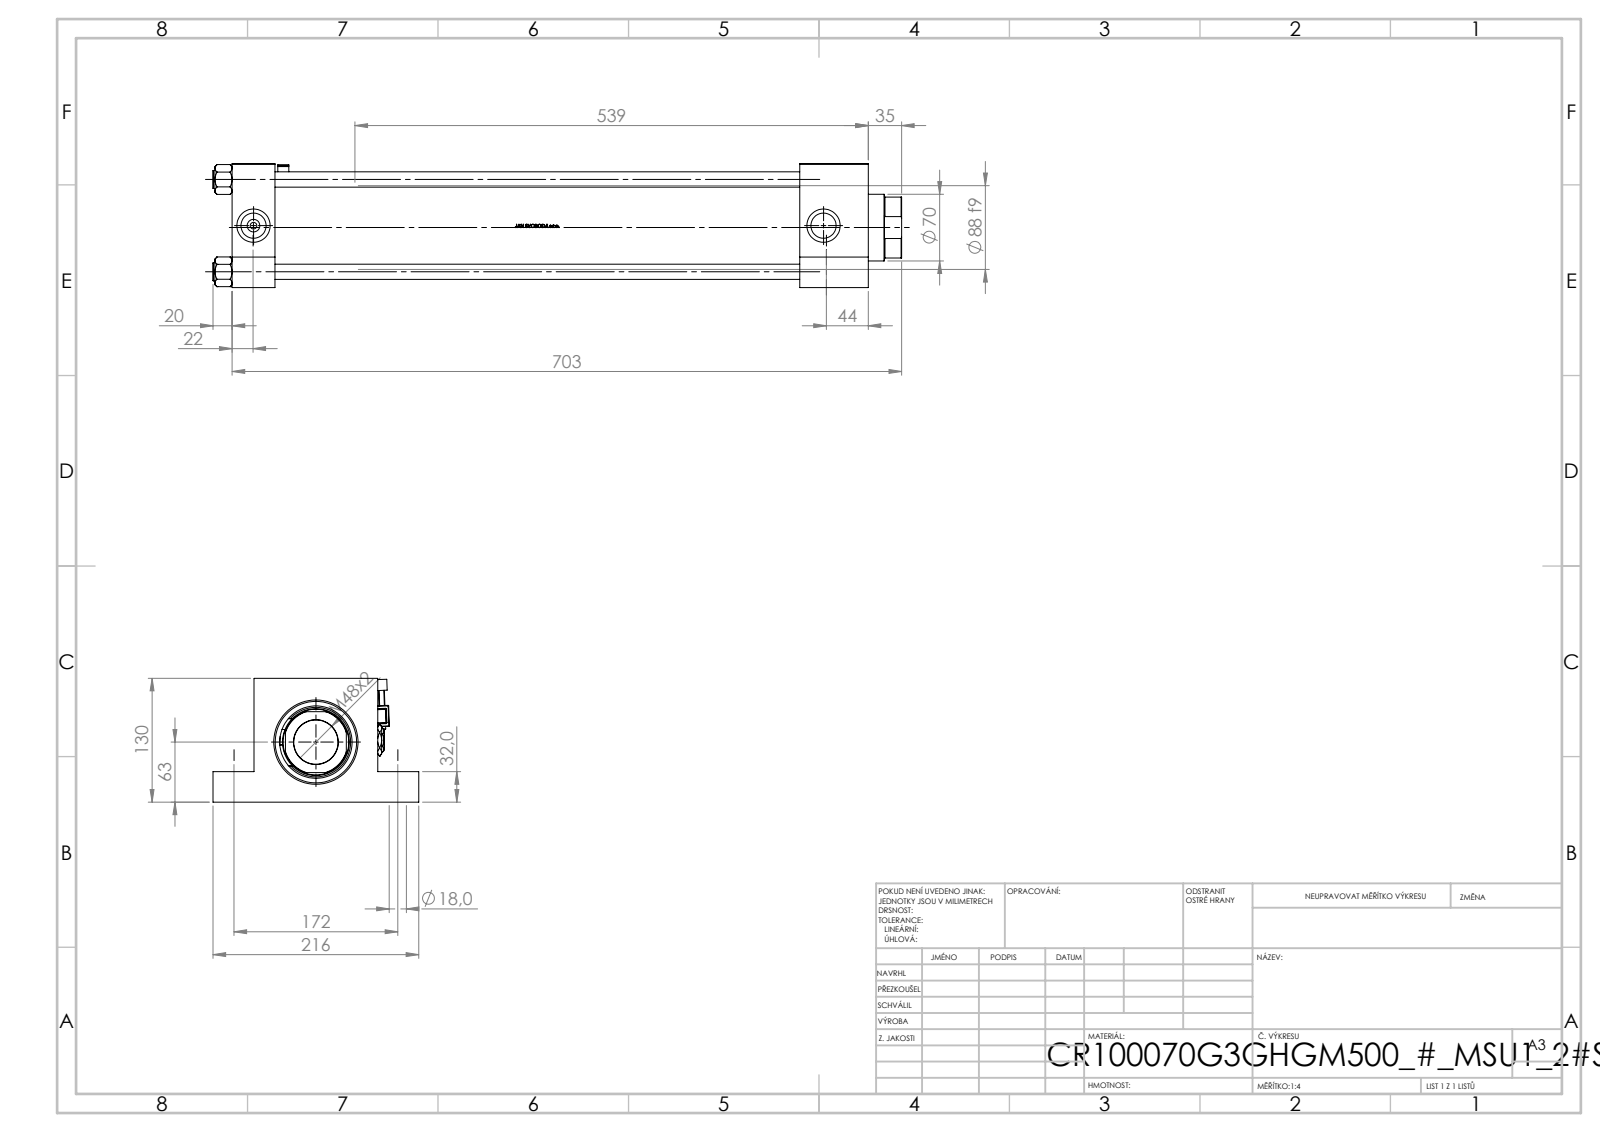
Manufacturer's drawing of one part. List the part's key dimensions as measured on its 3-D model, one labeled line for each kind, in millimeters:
Part name (STEP PRODUCT): V215CR_G_Body; NUT_M5_G; V215CR_MSU; V215_VC_A (+3 more)
STEP written by: SolidWorks 2019 (CONFIG_CONTROL_DESIGN)
Units: millimetres
Bodies: 15 solids, 1385 faces (583 planar, 192 cylindrical, 610 other)
Overall size (bounding box): 723 × 216 × 130
Volume: 5 615 000 mm³ · Surface area: 903 947 mm²
Round holes (diameter × count): ⌀16 ×4, ⌀18 ×4, ⌀7 ×2, ⌀26.44 ×2, ⌀35 ×2, ⌀46.5 ×1, ⌀70 ×1, ⌀73 ×1, ⌀76 ×1, ⌀85.5 ×1, ⌀100 ×1
Round bosses / shafts (diameter × count): ⌀19 ×4, ⌀6 ×2, ⌀106 ×1, ⌀88 ×1
Partial cylindrical surfaces — rounded edges, fillets, slot ends (radius × count): R0.5 ×48, R1 ×2, R2.5 ×2, R4 ×2, R8 ×1, R34 ×1
Main face-to-face distances: 130, 45, 596, 551, 668, 623, 72, 32, 98, 43
Hole centre spacings: 96.9, 67.12, 69.95, 137.04, 172, 602, 626.09, 598.5
